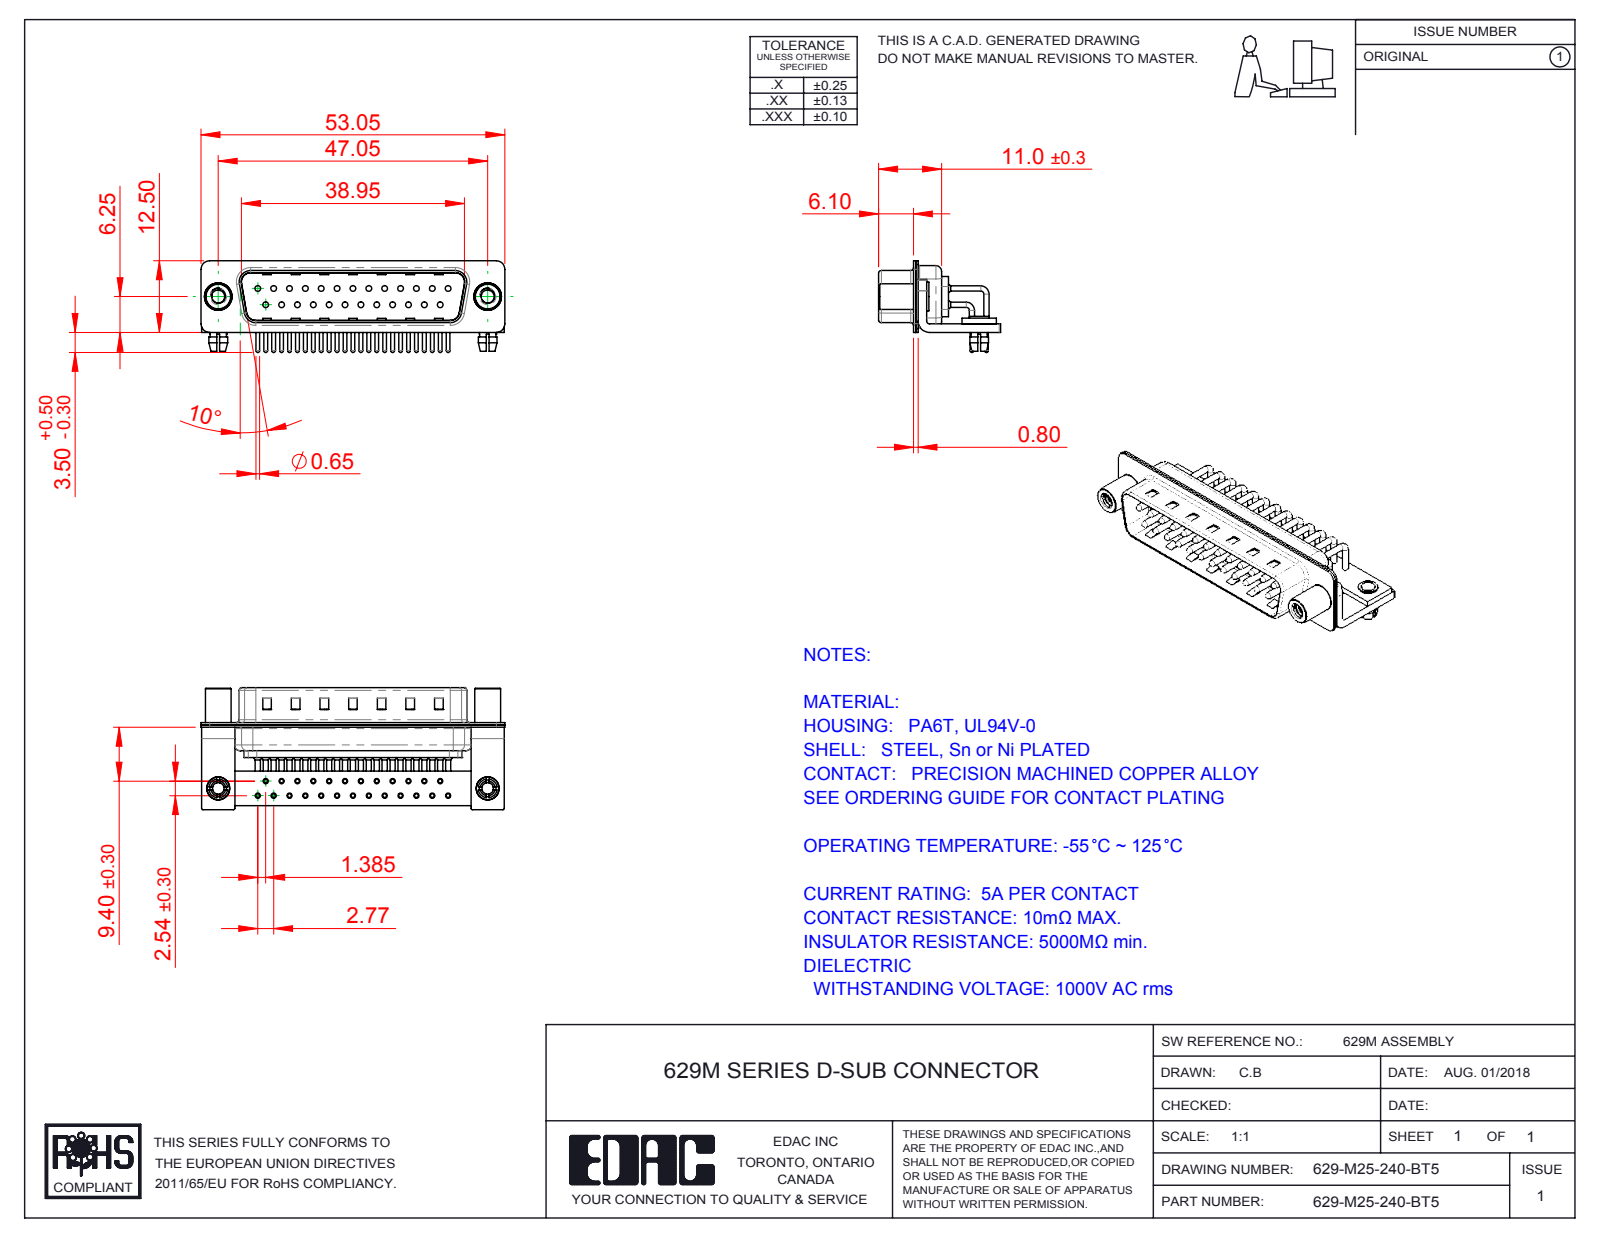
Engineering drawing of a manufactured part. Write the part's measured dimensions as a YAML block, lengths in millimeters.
part_name: "629M Contact Row 2; 629M Contact Row 1; 629M 4-40 Threaded Standoff; 629M Shell Rear_25 Contacts (+6 more)"
step_written_by: "SolidWorks 2016 (CONFIG_CONTROL_DESIGN)"
units: millimeters
bodies: {solids: 35, faces: 3368, planar: 1847, cylindrical: 1183, other: 338}
overall_size: [53.05, 21.3, 16]
volume: 3638
surface_area: 9694
round_holes:
  - {diameter: 2, count: 27}
  - {diameter: 0.9, count: 25}
  - {diameter: 1, count: 25}
  - {diameter: 1.7, count: 25}
  - {diameter: 2.26, count: 2}
  - {diameter: 2.5, count: 2}
  - {diameter: 3.2, count: 2}
  - {diameter: 4, count: 2}
  - {diameter: 4.8, count: 2}
round_bosses_or_shafts:
  - {diameter: 1.5, count: 25}
  - {diameter: 0.9, count: 25}
  - {diameter: 0.65, count: 25}
  - {diameter: 5, count: 2}
  - {diameter: 4.9, count: 2}
  - {diameter: 4.5, count: 2}
  - {diameter: 4, count: 2}
  - {diameter: 3.4, count: 2}
partial_cylinders:
  - {radius: 1.01, count: 25}
  - {radius: 0.25, count: 16}
  - {radius: 1.5, count: 16}
  - {radius: 2, count: 13}
  - {radius: 0.5, count: 9}
  - {radius: 1.6, count: 8}
  - {radius: 0.6, count: 4}
  - {radius: 0.65, count: 4}
face_to_face_distances: [0.4, 0.85, 1.25, 1.5, 9.55, 10.4, 0.8, 8.3, 1, 1.9]
hole_center_spacings: [2.77, 5.54, 8.31, 11.08, 13.85, 3.16, 4.87, 16.62]
